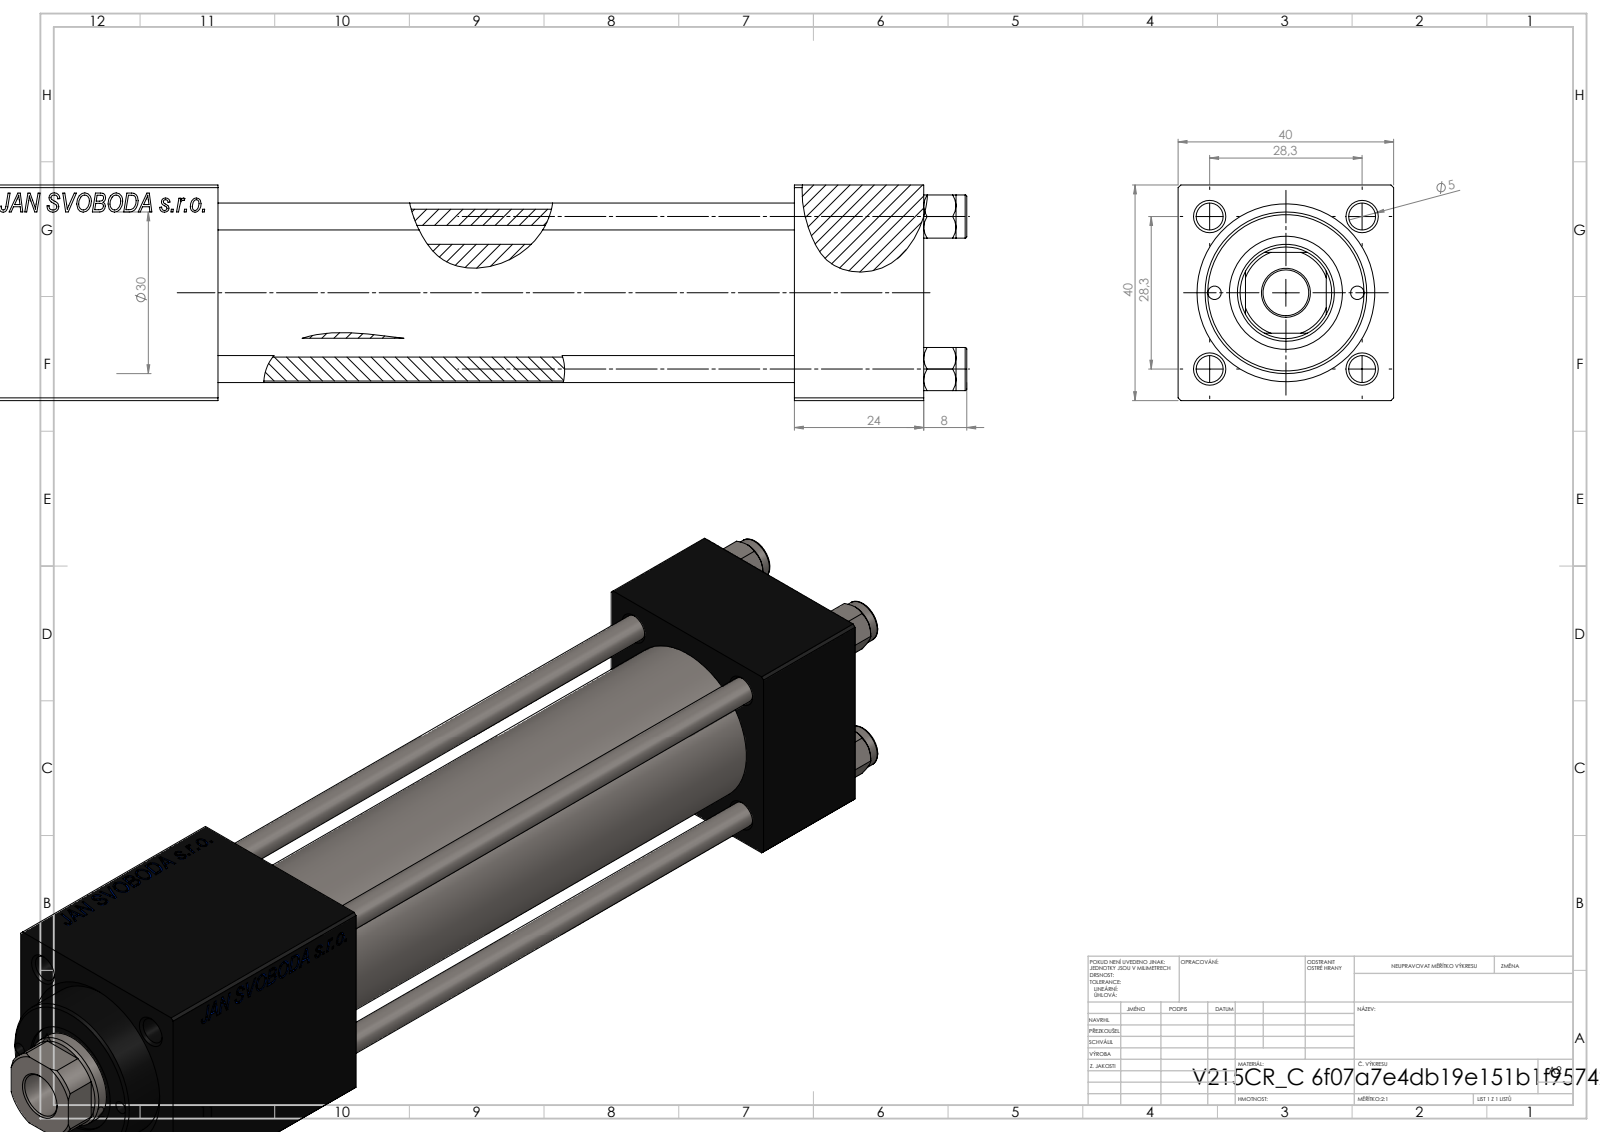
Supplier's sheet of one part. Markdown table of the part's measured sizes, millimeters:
| quantity | value |
| --- | --- |
| part name | V215_VC_A; V215CR_C_Body; V215CR_C_TYCINKA; NUT_M5_C (+1 more) |
| STEP written by | SolidWorks 2019 (CONFIG_CONTROL_DESIGN) |
| units | millimeters |
| bodies | 11 solids, 1150 faces (526 planar, 88 cylindrical, 536 other) |
| overall size | 202 × 40 × 40 |
| volume | 185 693 mm³ |
| surface area | 74 624 mm² |
| round holes (diameter × count) | 5 × 4, 20 × 3, 2.5 × 2, 7 × 2, 13.16 × 2, 8.5 × 1, 18 × 1, 21 × 1, 25 × 1, 30 × 1 |
| round bosses / shafts (diameter × count) | 8 × 4, 31 × 1 |
| partial cylindrical surfaces (radius × count) | 8.5 × 1 |
| main face-to-face distances | 40, 24, 131, 107, 150.3, 126.3, 19.3, 48, 179, 155 |
| hole center spacings | 14.18, 20.01, 28.3, 30.84, 13.25, 40.02, 26.5, 132 |
